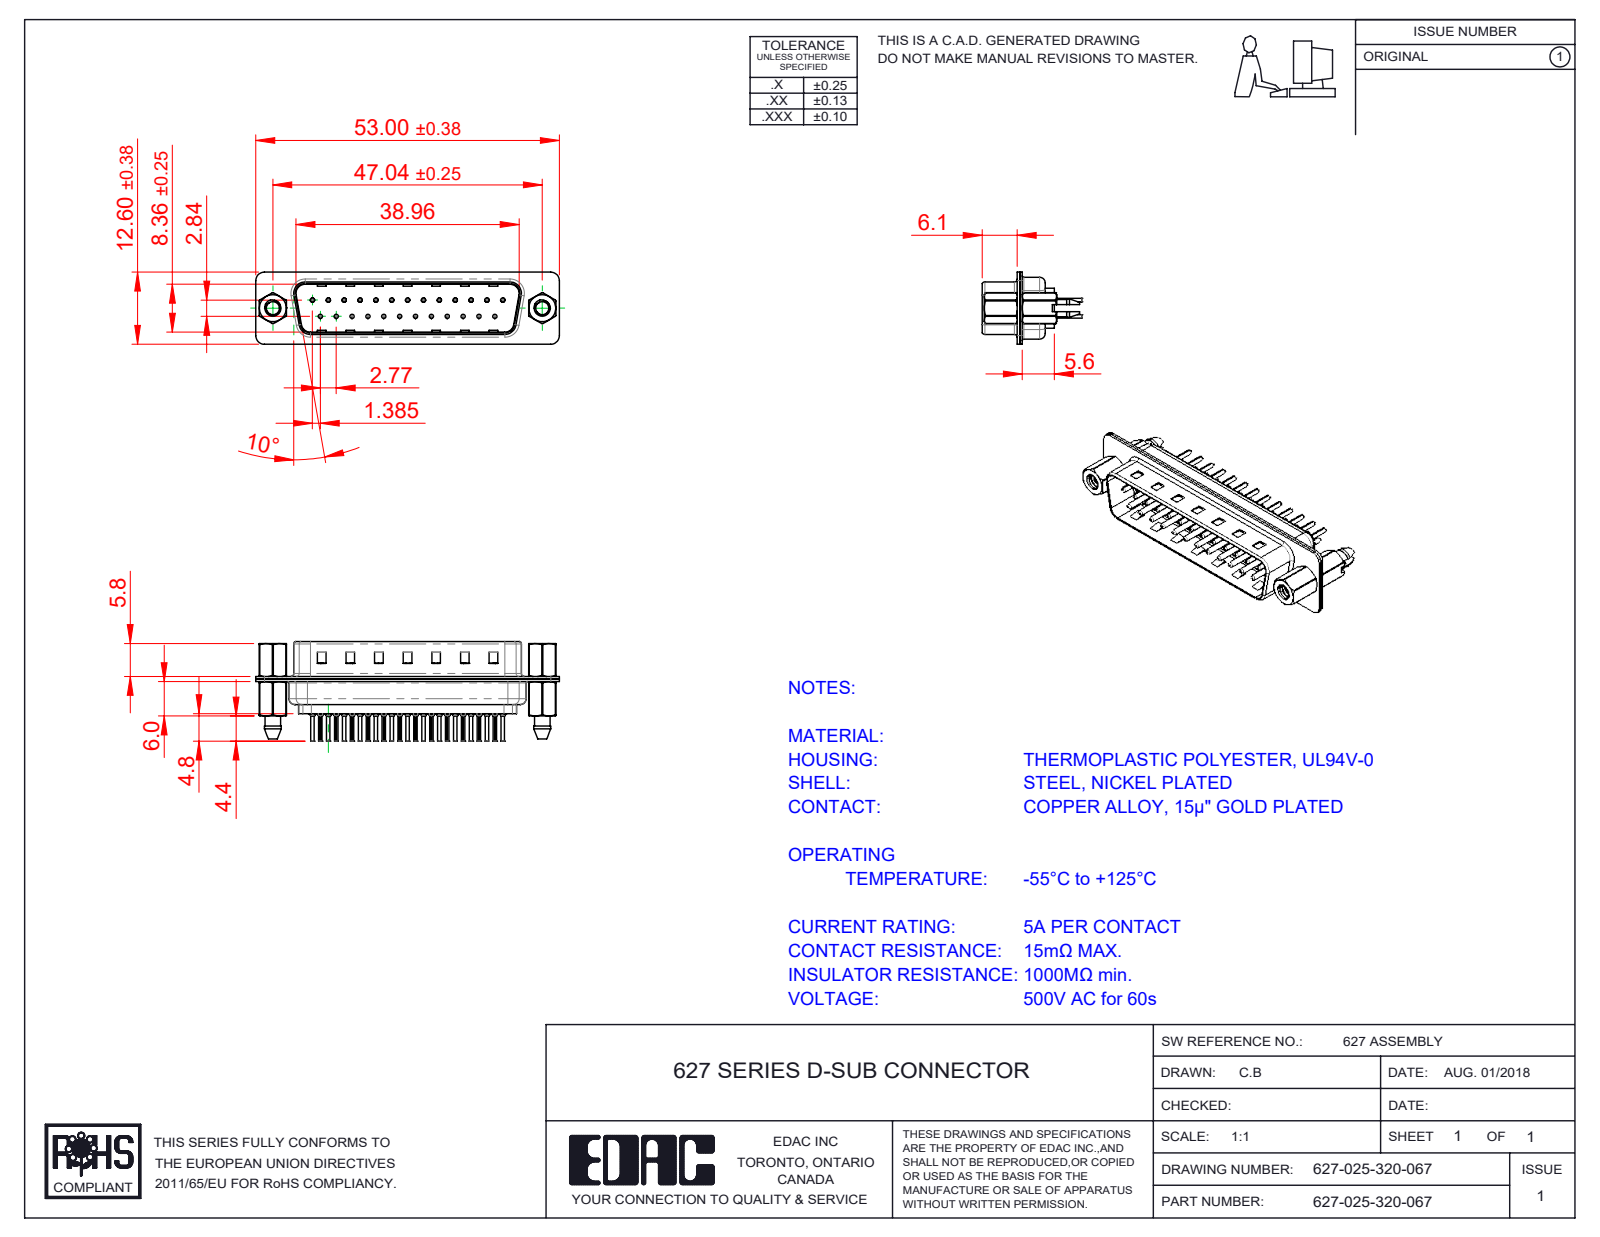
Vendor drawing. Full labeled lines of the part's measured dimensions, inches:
Part name (STEP PRODUCT): 627 Contact Row 2_20L; 627 Housing_25 LP; 627 4-40 Hex Standoff; 627 Shell Rear_25 Contacts (+4 more)
STEP written by: SolidWorks 2020 (CONFIG_CONTROL_DESIGN)
Units: inches
Bodies: 32 solids, 3026 faces (825 planar, 1166 cylindrical, 1035 other)
Overall size (bounding box): 2.087 × 0.681 × 0.496
Volume: 0.184 in³ · Surface area: 13.3 in²
Round holes (diameter × count): ⌀0.008 ×25, ⌀0.014 ×25, ⌀0.043 ×25, ⌀0.063 ×25, ⌀0.089 ×2, ⌀0.09 ×2, ⌀0.157 ×2, ⌀0.189 ×2
Round bosses / shafts (diameter × count): ⌀0.079 ×25, ⌀0.059 ×25, ⌀0.03 ×25, ⌀0.024 ×25, ⌀0.193 ×2, ⌀0.11 ×2
Partial cylindrical surfaces — rounded edges, fillets, slot ends (radius × count): R0.004 ×50, R0.059 ×18, R0.079 ×12, R0.063 ×10, R0.02 ×8, R0.01 ×4, R0.024 ×4, R0.026 ×4
Main face-to-face distances: 0.016, 0.018, 0.032, 0.377, 0.345, 0.035, 0.059, 0.055, 0.256, 0.238
Hole centre spacings: 0.124, 0.327, 0.109, 0.218, 0.436, 0.654, 0.198, 0.198
